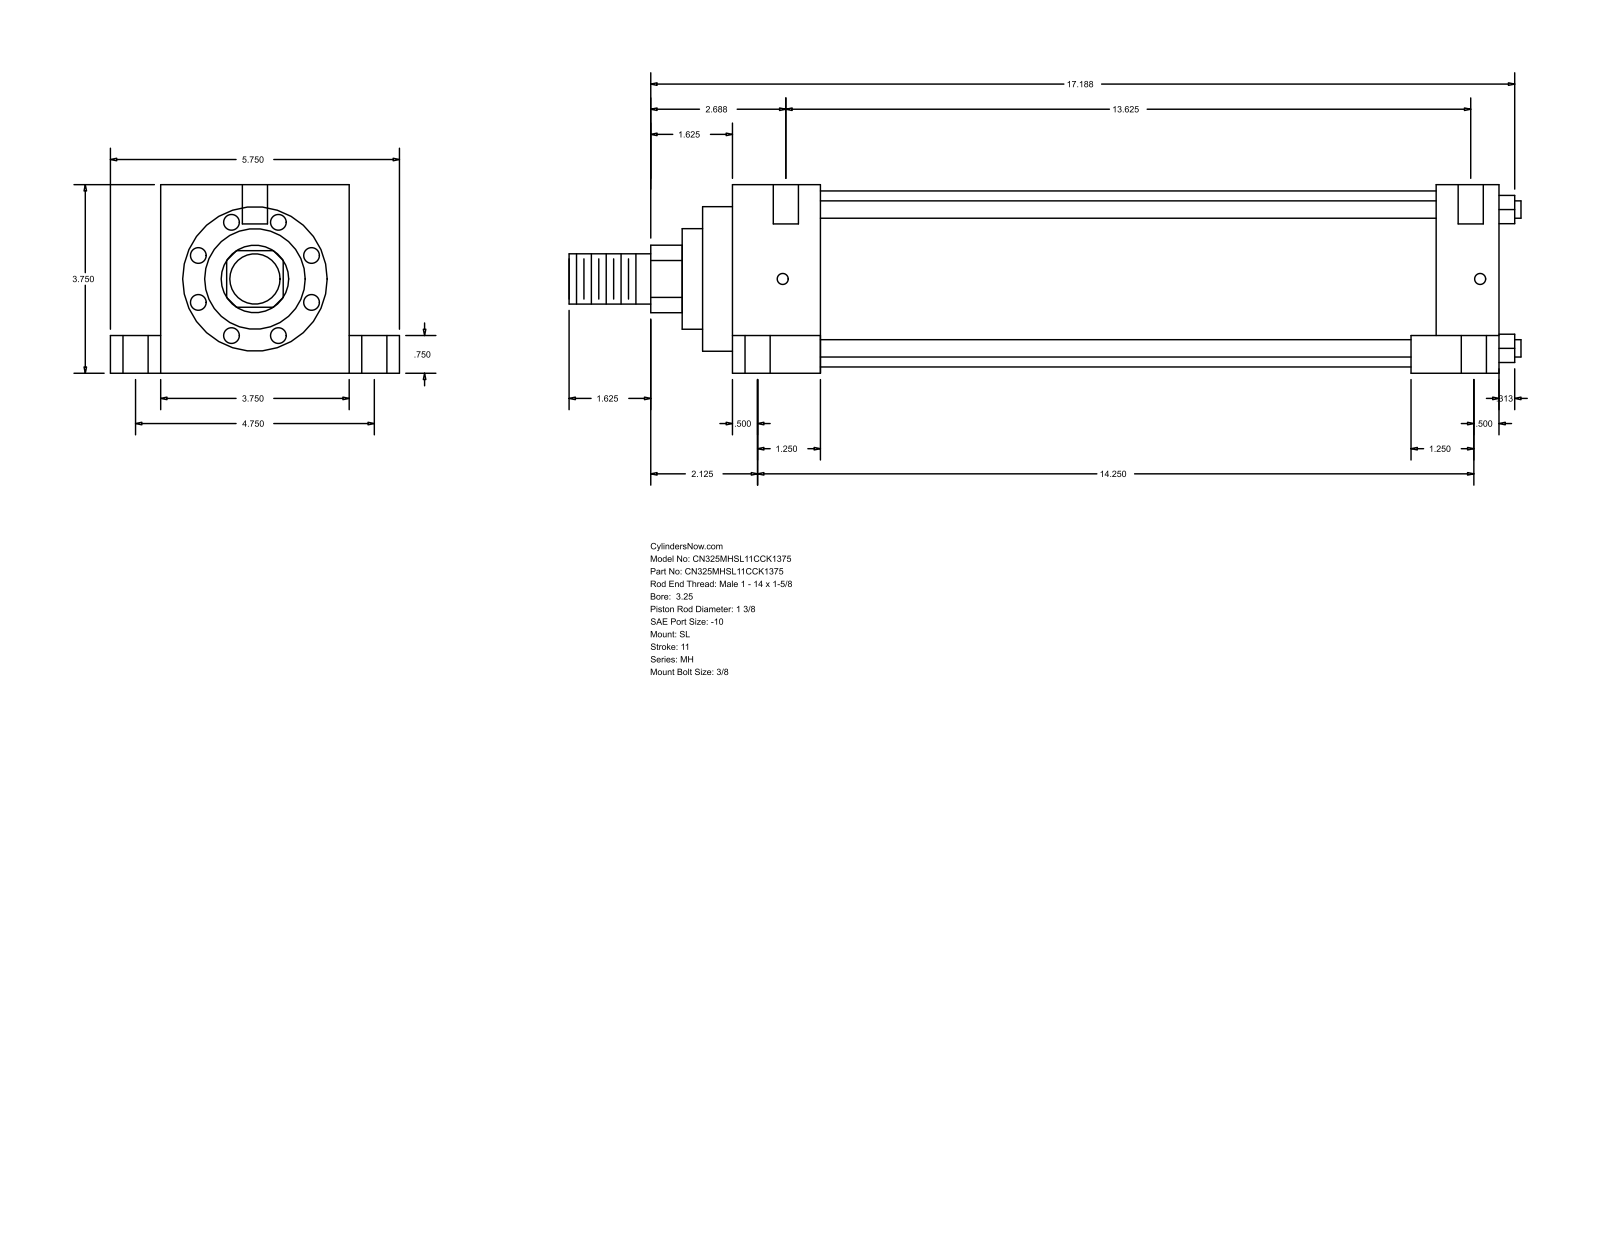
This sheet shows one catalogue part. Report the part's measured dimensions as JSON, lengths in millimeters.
{"part_name": "MH_SL__0325_1.375", "step_written_by": "GSSL Pune (CONFIG_CONTROL_DESIGN)", "units": "millimeters", "bodies": {"solids": 0, "faces": 110, "planar": 77, "cylindrical": 33, "other": 0}, "overall_size": [481.01, 146.05, 95.25], "round_holes": [[12.7, 6], [5.56, 4], [19.05, 4]], "round_bosses_or_shafts": [[8.76, 4], [88.9, 1], [73.03, 1], [50.8, 1], [34.92, 1], [25.4, 1]], "partial_cylinders_radius": [[17.06, 1]], "face_to_face_distances": [95.24, 387.35, 44.45, 342.9, 25.41, 120.65, 19.05, 76.19, 355.61, 311.16], "hole_center_spacings": [60.35, 60.41, 61.65, 62, 120.66, 352.43, 352.87, 354.43]}
